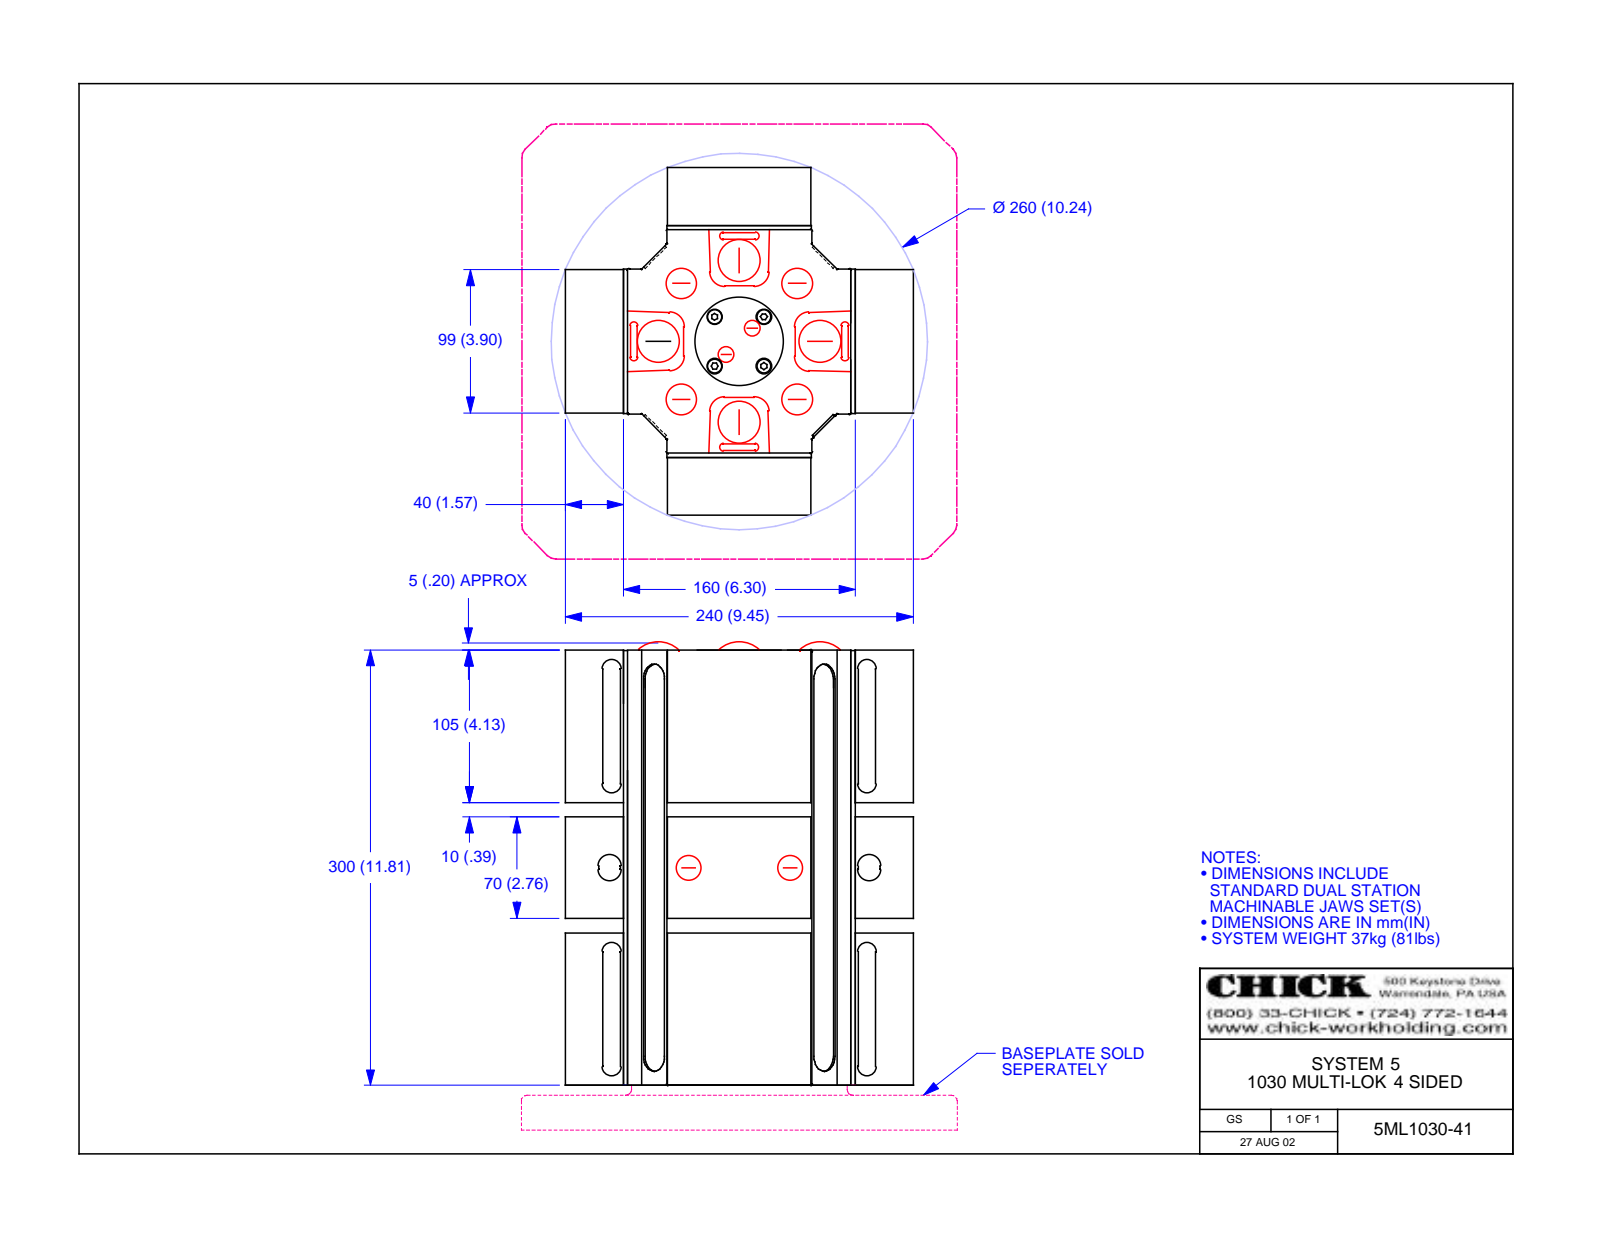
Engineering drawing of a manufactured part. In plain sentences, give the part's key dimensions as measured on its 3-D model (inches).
The part is named "5ML1030-41; 5CLM1030-41CM; 5CP1030-ST; 5DS1030-10-40 (+2 more)". Its 3-D file was written by "Autodesk Inventor 2013 (AUTOMOTIVE_DESIGN)". It is 17 solids with 2511 faces: 1258 planar, 484 cylindrical and 769 other. Overall it measures 12.028 by 9.425 by 9.425 inches. Its volume is 587 cubic inches and its surface area 1 556 square inches. Round holes: 12 of diameter 0.262, 12 of diameter 0.354, 12 of diameter 0.557, 12 of diameter 0.761, 8 of diameter 0.341, 8 of diameter 0.398, 8 of diameter 0.5, 6 of diameter 0.394, 4 of diameter 0.16, 4 of diameter 0.194, 4 of diameter 0.27, 4 of diameter 0.331. Round bosses or shafts: 8 of diameter 0.331, 4 of diameter 0.302, 4 of diameter 0.187. Partial cylindrical surfaces (rounded edges, fillets, slot ends): 88 of radius 0.059, 16 of radius 0.016, 16 of radius 0.047, 16 of radius 0.189, 16 of radius 0.437, 8 of radius 0.065, 8 of radius 0.111, 8 of radius 0.118. The main face-to-face distances are 0.118, 6.181, 1.563, 1.681, 7.744, 7.862, 6.063, 6.299, 4.24, 5.185. The hole center spacings are 2.756, 0.048, 1.004, 1.378, 1.797, 2.307, 2.645, 2.774.
